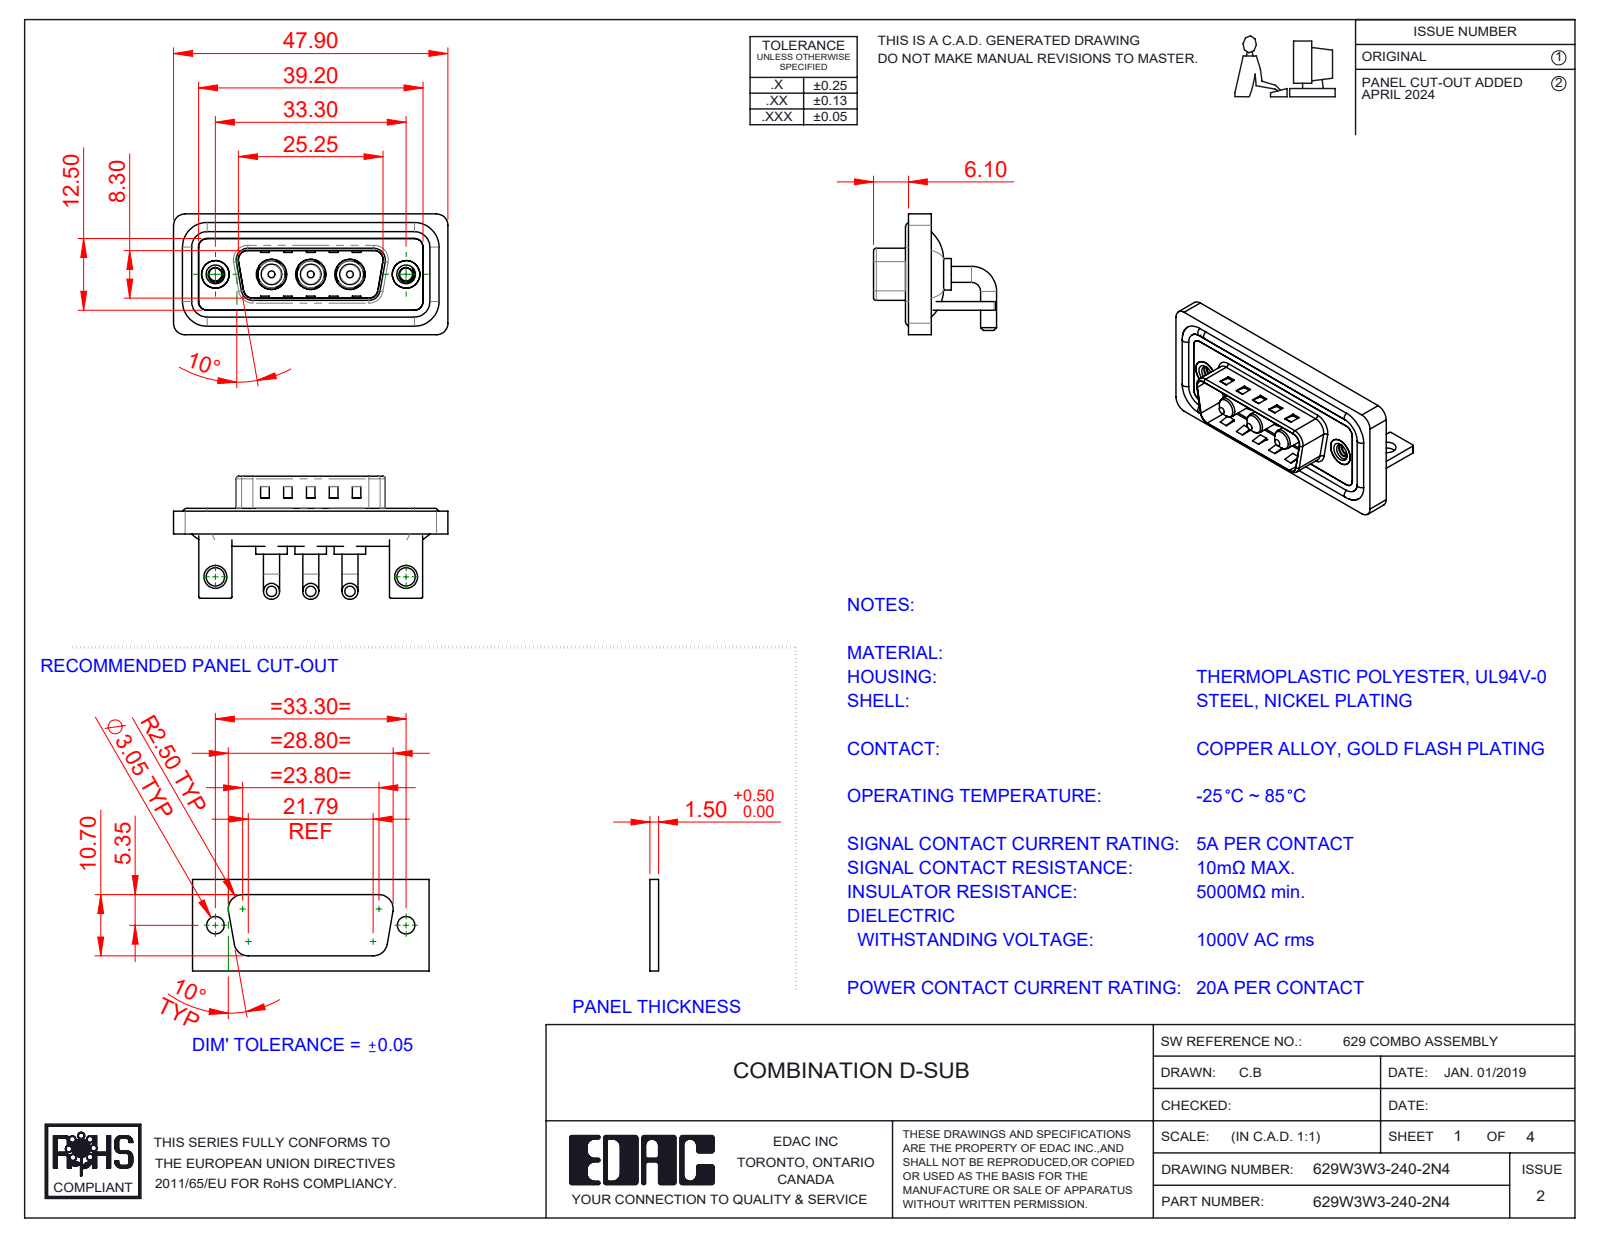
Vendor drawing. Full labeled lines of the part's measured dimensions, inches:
Part name (STEP PRODUCT): 629Combo Shell Rear_15 Contacts; 629W3W3-240-2N4; 629Combo Stabilizer Bracket; Power Pin_20A RA (+4 more)
STEP written by: SolidWorks 2023 (CONFIG_CONTROL_DESIGN)
Units: inches
Bodies: 15 solids, 616 faces (227 planar, 265 cylindrical, 124 other)
Overall size (bounding box): 1.886 × 0.846 × 0.831
Volume: 0.37 in³ · Surface area: 14.92 in²
Round holes (diameter × count): ⌀0.191 ×3, ⌀0.209 ×3, ⌀0.089 ×2, ⌀0.126 ×2, ⌀0.157 ×2, ⌀0.189 ×2, ⌀0.197 ×2
Round bosses / shafts (diameter × count): ⌀0.11 ×6, ⌀0.063 ×4, ⌀0.217 ×3, ⌀0.205 ×3, ⌀0.187 ×3, ⌀0.148 ×3, ⌀0.142 ×3, ⌀0.193 ×2
Partial cylindrical surfaces — rounded edges, fillets, slot ends (radius × count): R0.079 ×21, R0.059 ×18, R0.01 ×16, R0.02 ×9, R0.063 ×8, R0.024 ×4, R0.026 ×4, R0.035 ×4
Main face-to-face distances: 0.016, 0.059, 0.031, 0.114, 0.043, 0.083, 0.146, 0.063, 0.047, 0.177
Hole centre spacings: 0.27, 0.386, 0.656, 0.925, 1.311, 0.539
